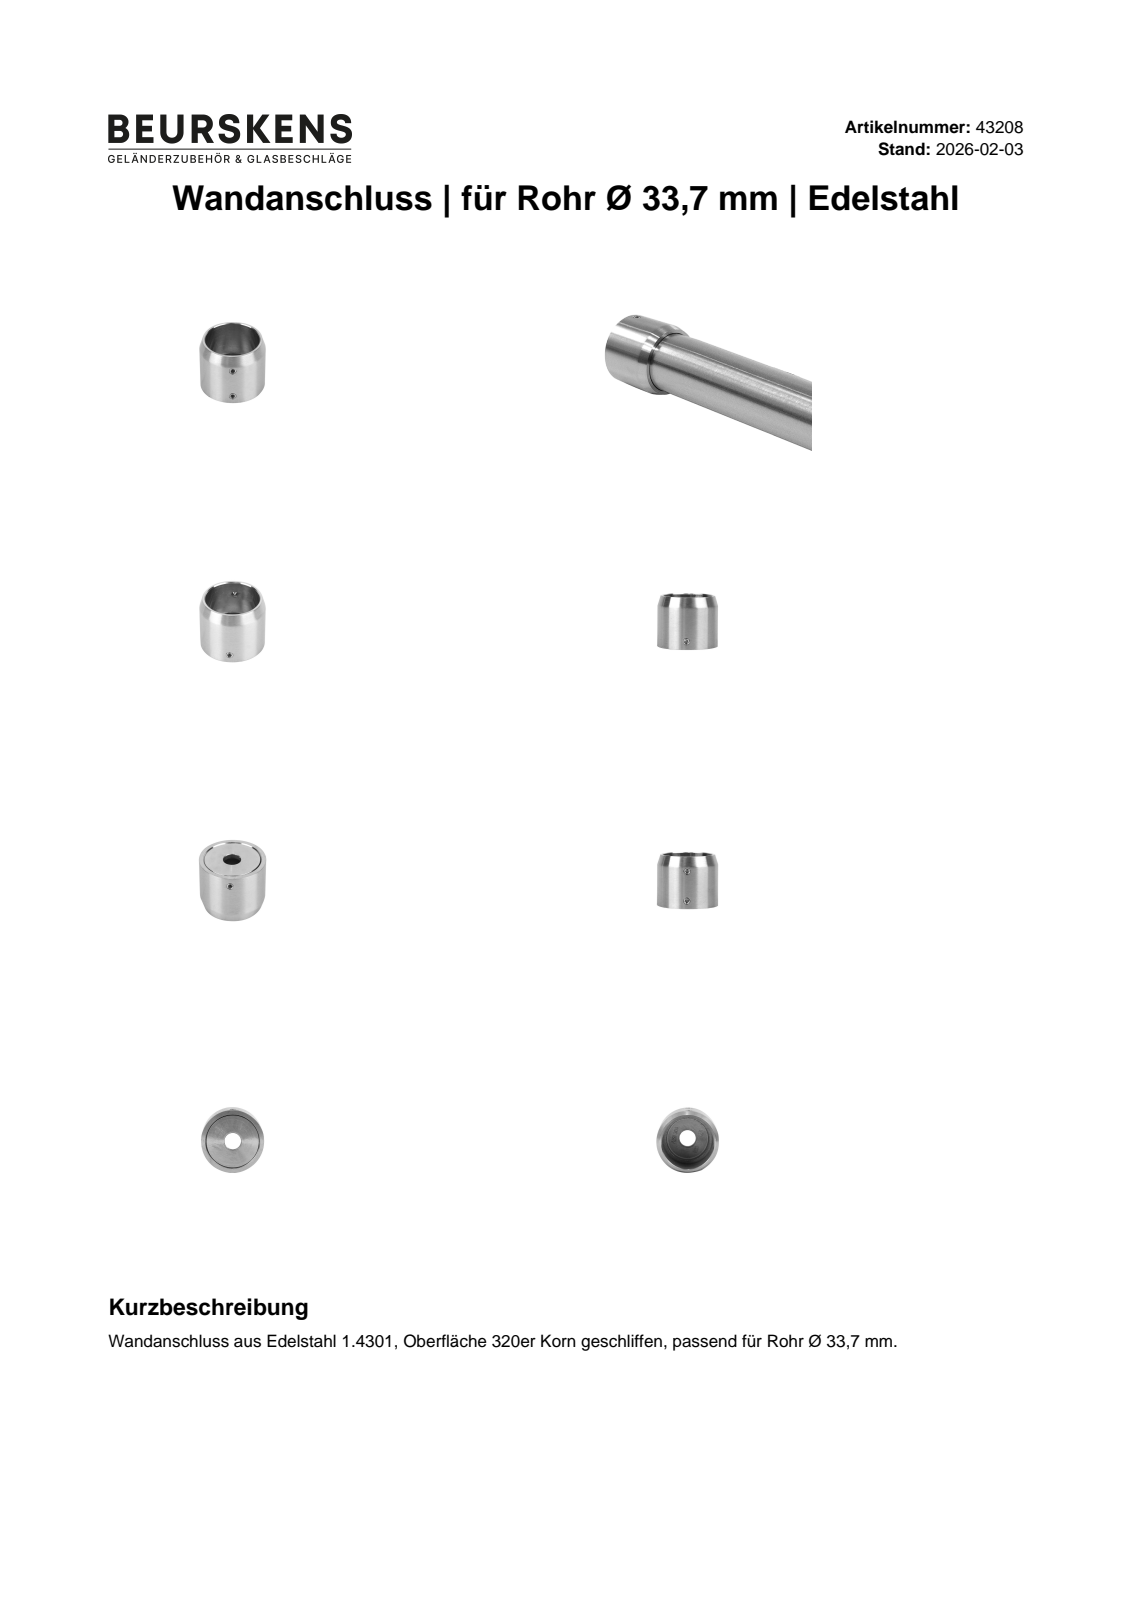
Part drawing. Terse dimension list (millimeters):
name: 43208; 41870_01; 43208_02; DIN 913 - M5 x 5
written by: Autodesk Inventor 2022 (AUTOMOTIVE_DESIGN)
unit: mm
bodies: 5 solids, 58 faces (30 planar, 13 cylindrical, 15 other)
size: 42.54 × 42 × 35
volume: 20 711 mm³; area: 12 951 mm²
holes: 2× ⌀4.8, 1× ⌀11, 1× ⌀29, 1× ⌀34
bosses: 2× ⌀5, 1× ⌀42, 1× ⌀35
face distances: 4.9, 9.8, 35, 30.1, 25.2, 2.5, 10, 5, 32.35, 32.53
hole spacings: 20
